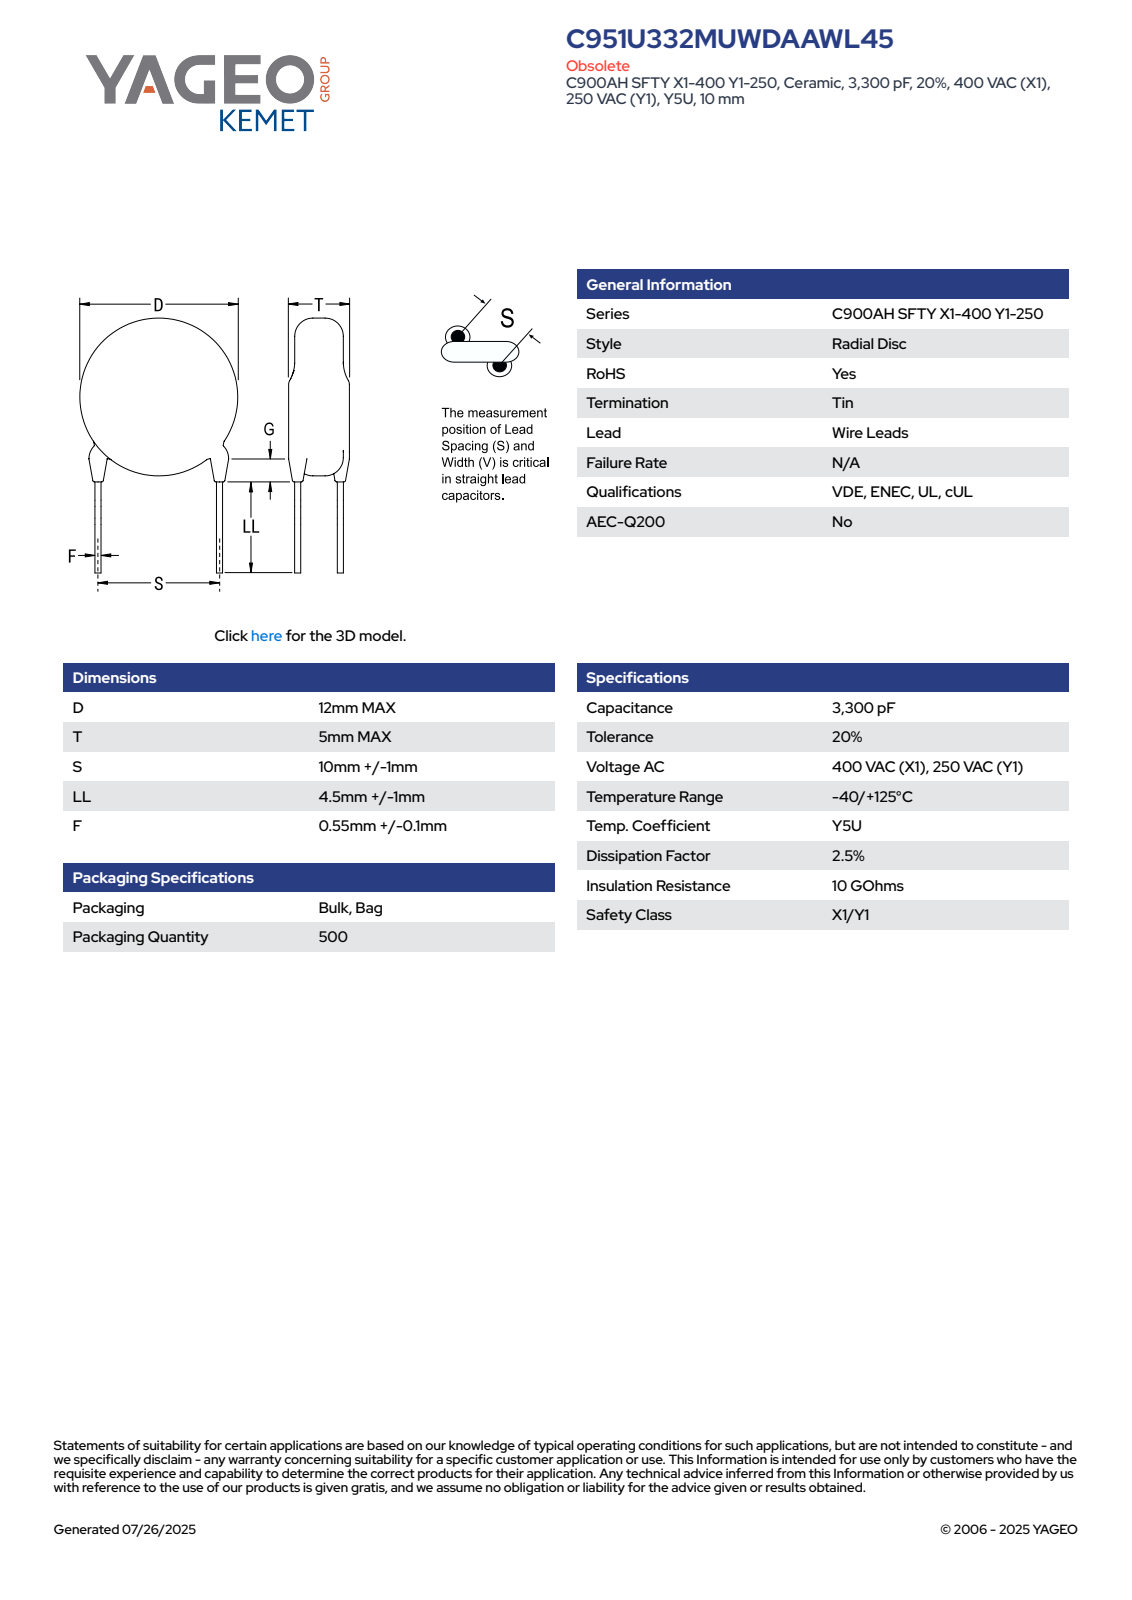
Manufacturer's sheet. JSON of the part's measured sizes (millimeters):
{"part_name": "CCD_STC900_D12T5S10LL5.5F0.65G3", "step_written_by": "SolidWorks 2014 (AUTOMOTIVE_DESIGN)", "units": "millimeters", "bodies": {"solids": 4, "faces": 83, "planar": 61, "cylindrical": 6, "other": 16}, "overall_size": [17.83, 12, 5], "volume_mm3": 557, "surface_area_mm2": 427, "round_bosses_or_shafts": [[0.65, 2], [12, 1]], "face_to_face_distances": [5, 12.52, 11.14, 1.38, 0.38, 0.34, 0.6, 5.66, 1.12, 0.86]}
